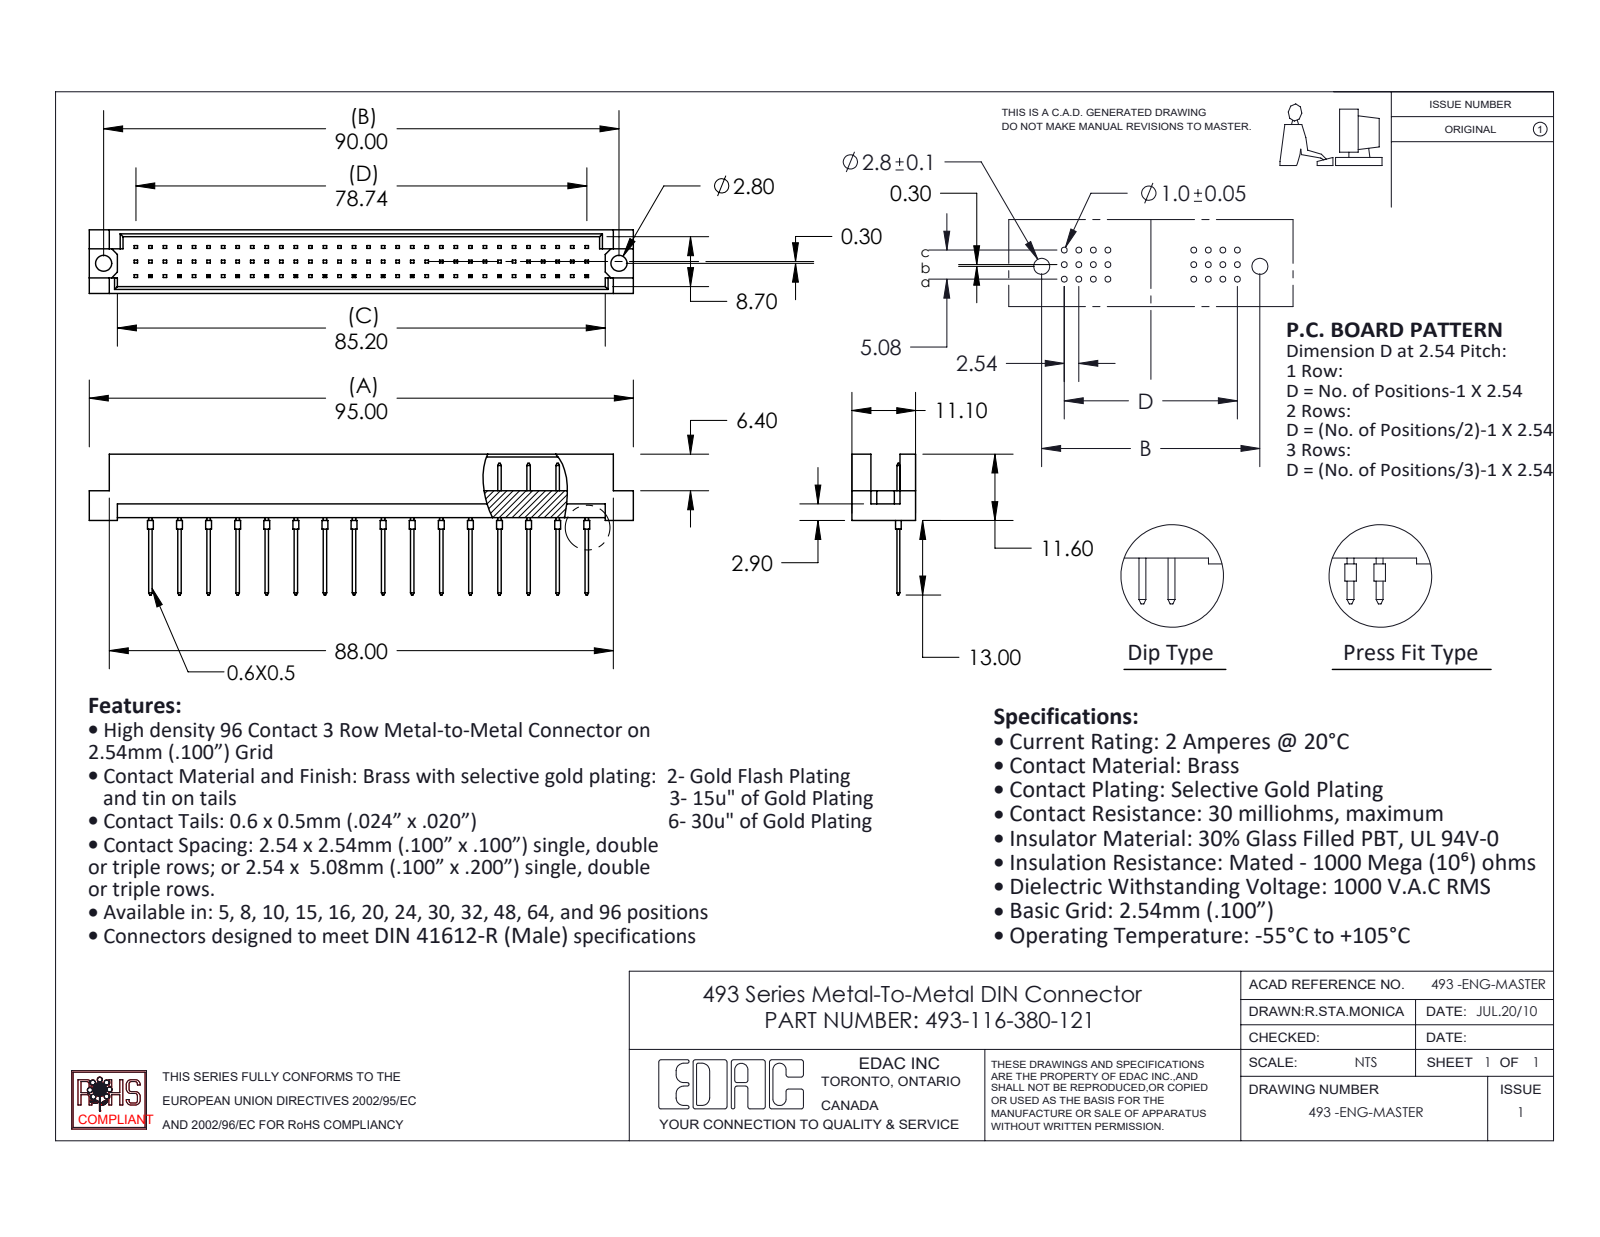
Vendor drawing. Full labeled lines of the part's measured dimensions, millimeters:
Part name (STEP PRODUCT): 493-290_80; 493-116-380-621; 493 Part_96
STEP written by: SolidWorks 2020 (CONFIG_CONTROL_DESIGN)
Units: millimetres
Bodies: 17 solids, 788 faces (752 planar, 36 cylindrical, 0 other)
Overall size (bounding box): 95 × 24.6 × 11.1
Volume: 5 780 mm³ · Surface area: 7 316 mm²
Round holes (diameter × count): ⌀2.8 ×2
Round bosses / shafts (diameter × count): ⌀1 ×16
Main face-to-face distances: 1.2, 9.9, 11.1, 8.7, 4.7, 0.5, 5.08, 2.76, 3.26, 7.84
Hole centre spacings: 90
